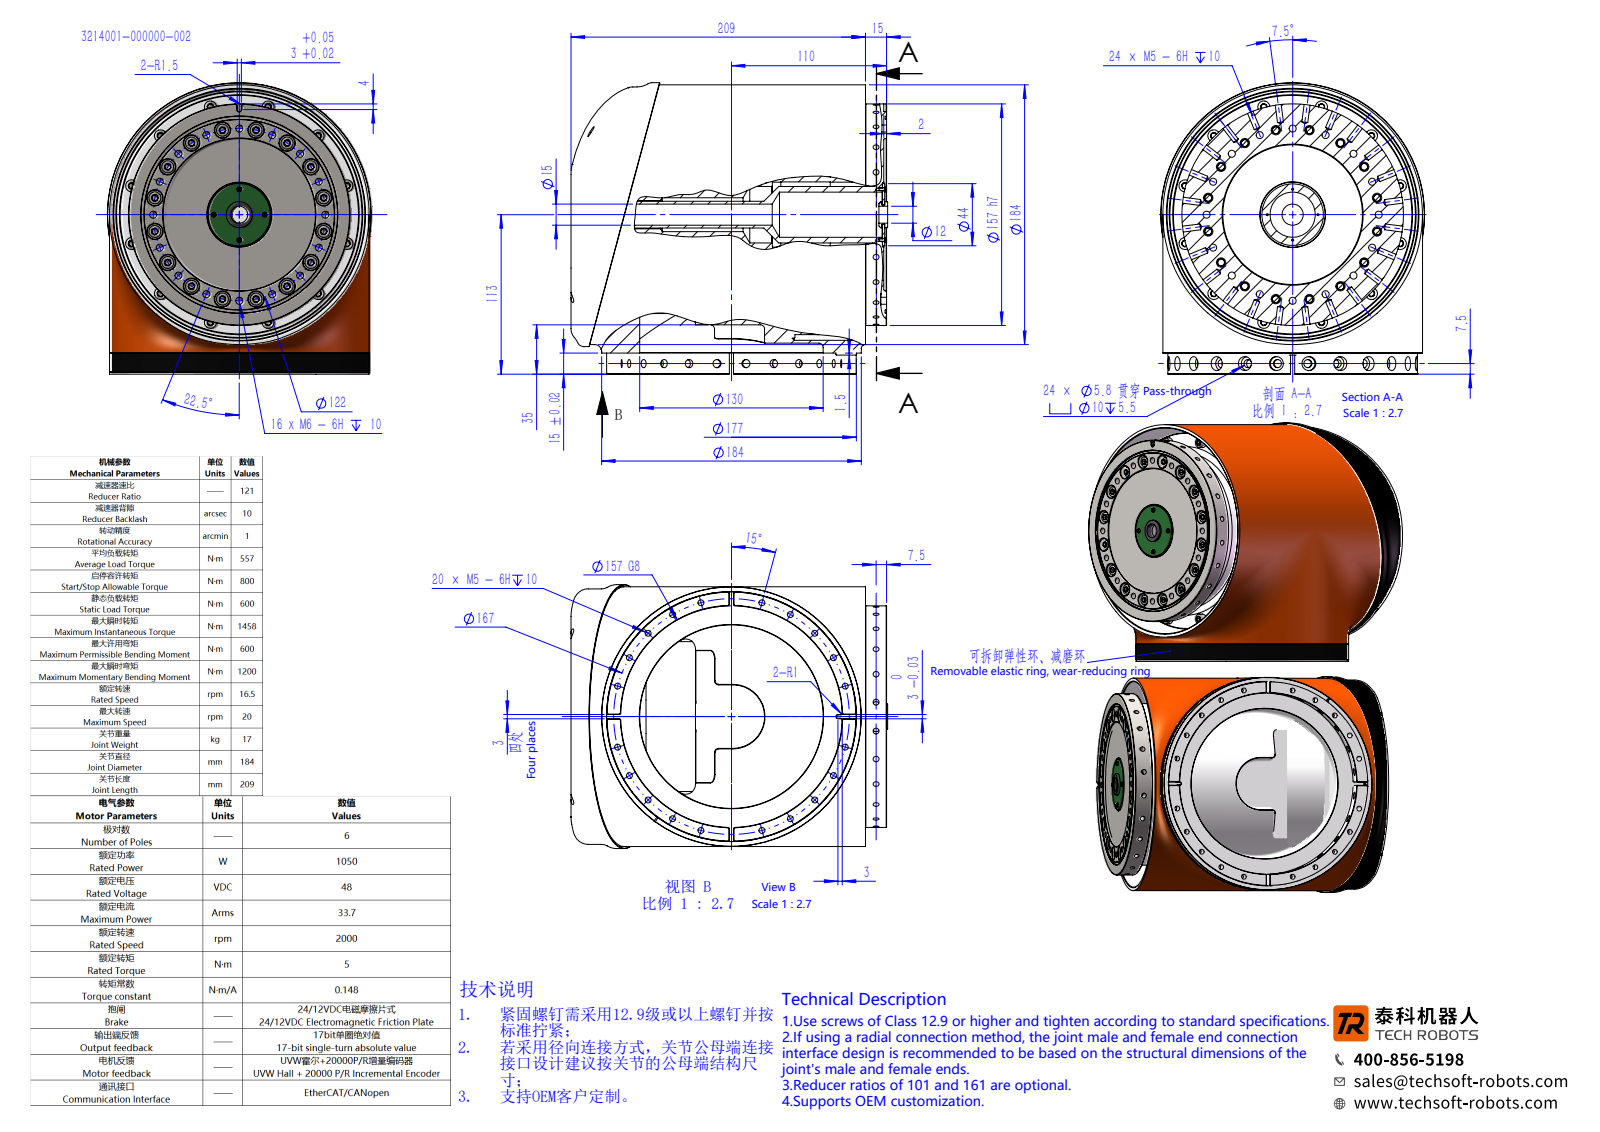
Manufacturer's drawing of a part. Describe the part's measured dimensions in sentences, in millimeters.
Its 3-D file was written by "SolidWorks 2016 (CONFIG_CONTROL_DESIGN)". It is 15 solids with 2184 faces: 697 planar, 726 cylindrical and 761 other. Overall it measures 224.42 by 206.5 by 187 millimeters. Its volume is 5 715 000 cubic millimeters and its surface area 342 557 square millimeters. Round holes: 51 of diameter 4.2, 33 of diameter 5, 30 of diameter 10, 28 of diameter 6.6, 24 of diameter 5.8, 16 of diameter 11, 6 of diameter 5.5, 4 of diameter 1.6, 4 of diameter 2.4, 4 of diameter 3.4, 4 of diameter 7, 1 of diameter 4.5. Round bosses or shafts: 28 of diameter 8.5, 28 of diameter 4.83, 4 of diameter 3.5, 4 of diameter 2, 1 of diameter 187, 1 of diameter 184.02, 1 of diameter 184, 1 of diameter 177. Partial cylindrical surfaces (rounded edges, fillets, slot ends): 18 of radius 1, 6 of radius 4.25, 5 of radius 2.25, 5 of radius 3, 4 of radius 1.5, 2 of radius 7, 1 of radius 22.5, 1 of radius 81. The main face-to-face distances are 15, 13, 182.72, 39, 221.72, 2, 41, 223.72, 26, 208.72. The hole center spacings are 61, 23.8, 83.5, 118.08, 46.69, 67.78, 86.27, 21.8.
